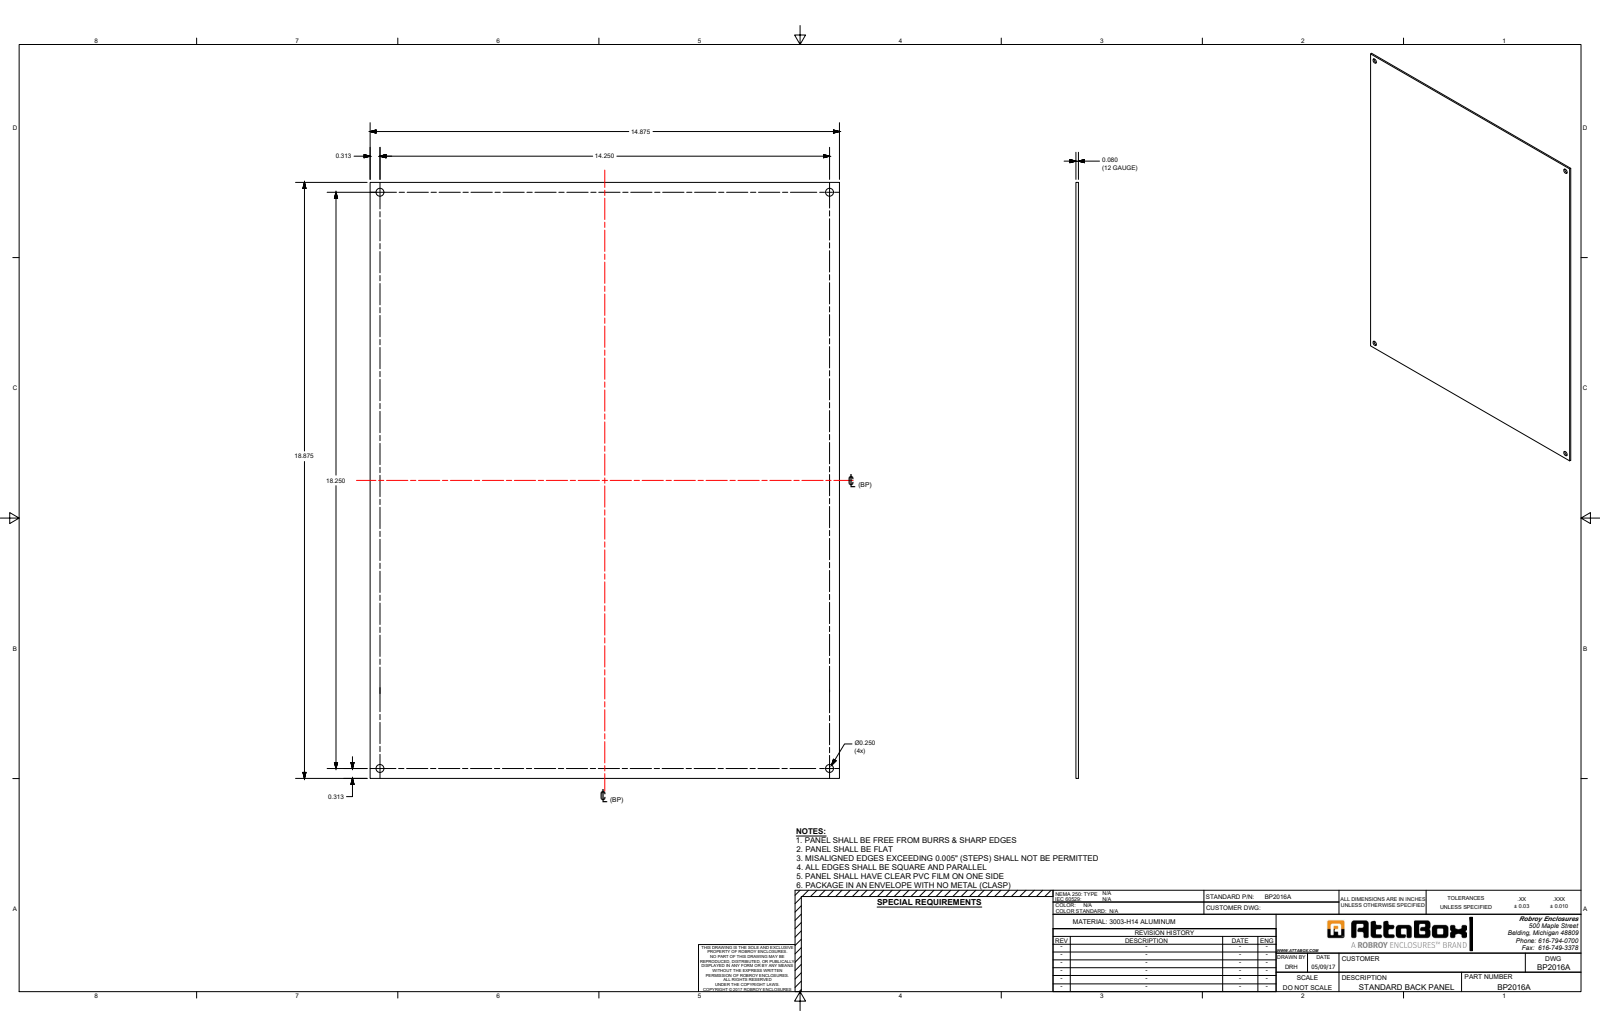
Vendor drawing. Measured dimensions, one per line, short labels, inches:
name: BP2016A
written by: SolidWorks 2023 (AUTOMOTIVE_DESIGN)
unit: in
bodies: 1 solid, 10 faces (6 planar, 4 cylindrical, 0 other)
size: 18.875 × 14.875 × 0.08
volume: 22.45 in³; area: 566.8 in²
holes: 4× ⌀0.25
face distances: 0.08, 14.875, 18.875
hole spacings: 14.25, 18.25, 23.154
